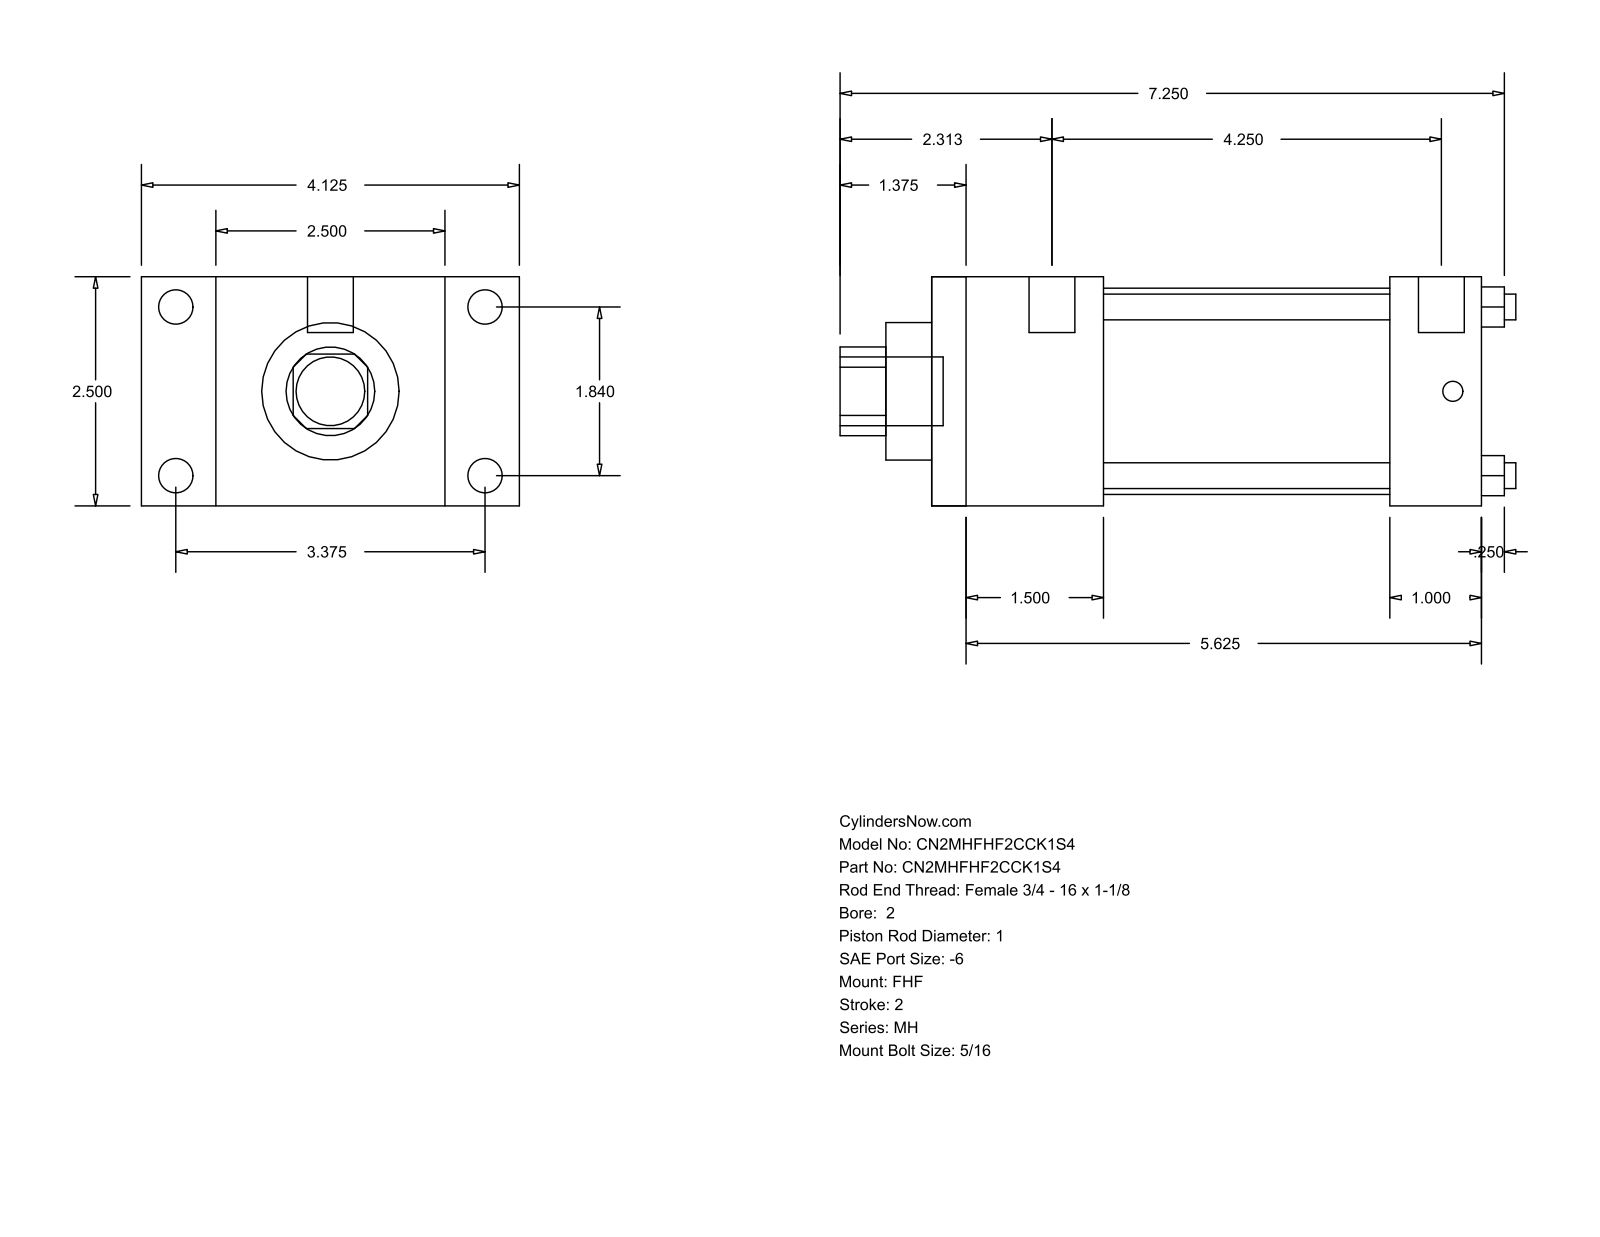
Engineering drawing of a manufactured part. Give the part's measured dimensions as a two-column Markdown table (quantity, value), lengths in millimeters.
| quantity | value |
| --- | --- |
| part name | MH_FHF__0200_1 |
| STEP written by | GSSL Pune (CONFIG_CONTROL_DESIGN) |
| units | millimeters |
| bodies | 0 solids, 88 faces (60 planar, 28 cylindrical, 0 other) |
| overall size | 187.32 × 104.78 × 63.5 |
| round holes (diameter × count) | 7.14 × 4, 25.4 × 1, 38.1 × 1, 57.15 × 1 |
| round bosses / shafts (diameter × count) | 9.53 × 4, 5.56 × 4, 12.7 × 2, 19.05 × 1 |
| partial cylindrical surfaces (radius × count) | 12.29 × 1 |
| main face-to-face distances | 63.5, 152.4, 104.77, 47.63, 20.64, 84.14, 104.78, 25.4, 127, 79.37 |
| hole center spacings | 33.05, 46.74, 66.1 |
